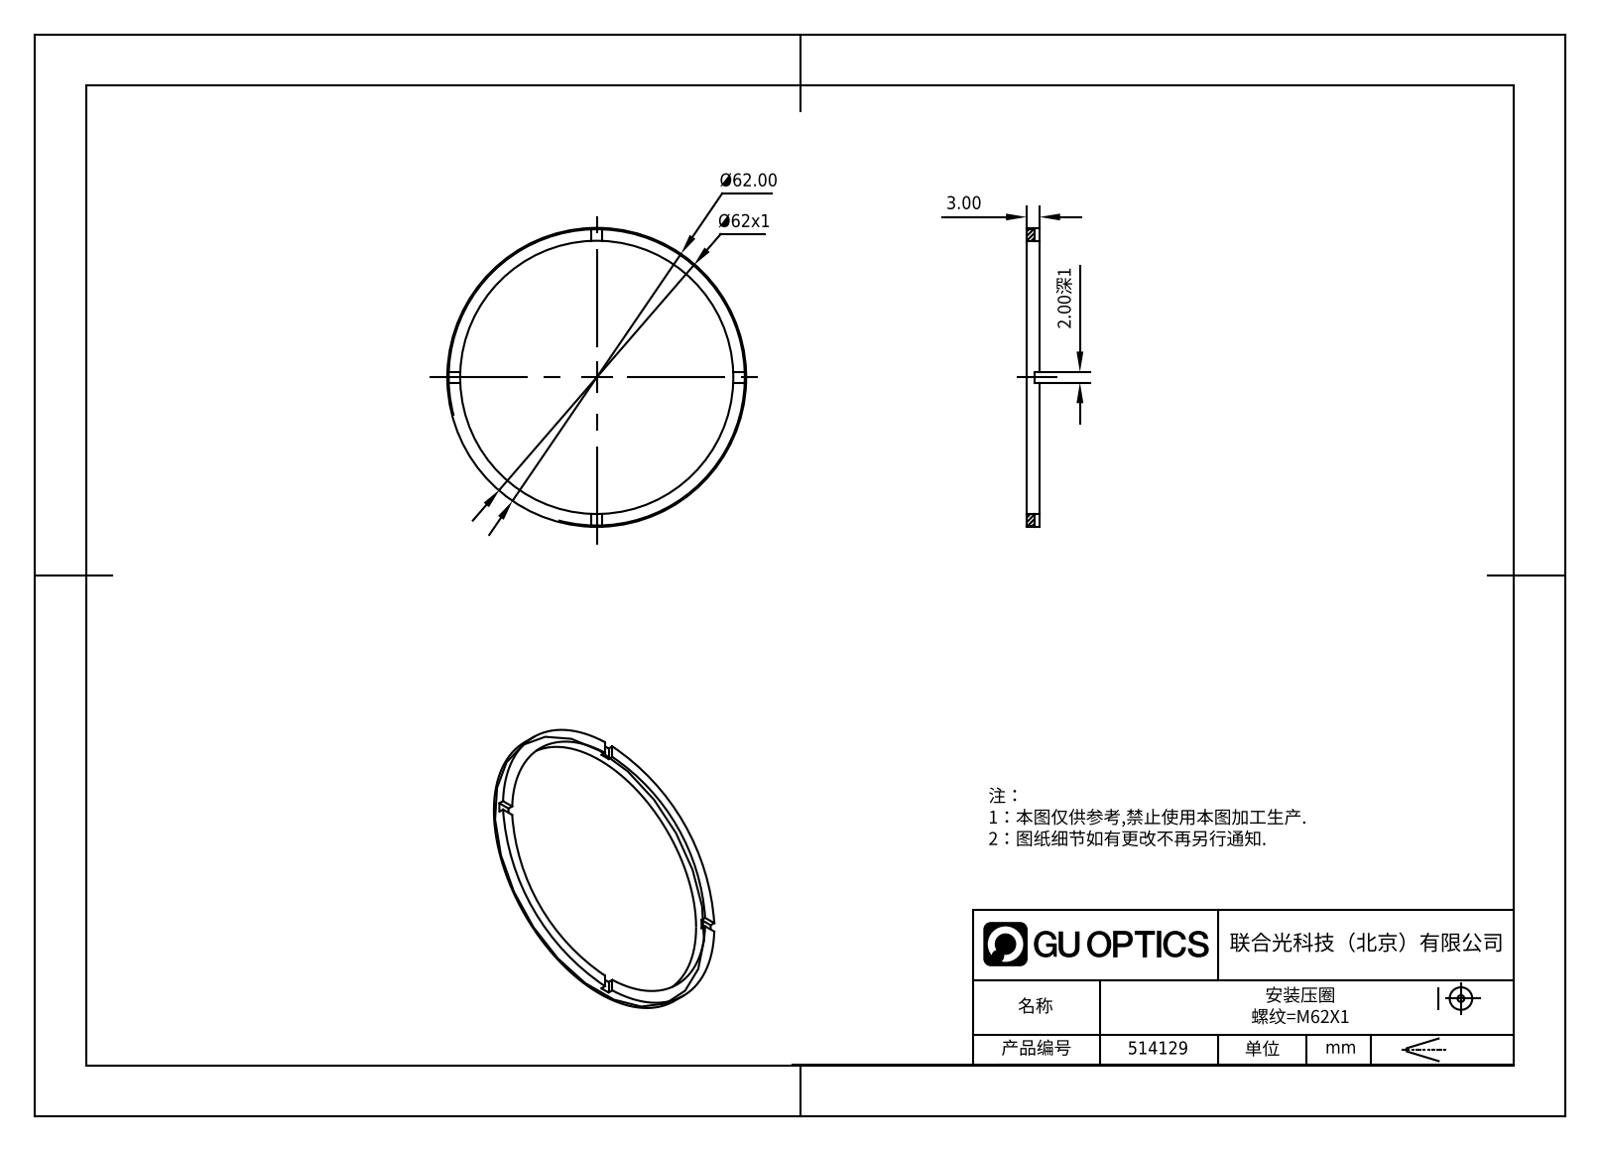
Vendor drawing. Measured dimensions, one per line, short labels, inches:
name: 514129
written by: SolidWorks 2020 (CONFIG_CONTROL_DESIGN)
unit: in
bodies: 1 solid, 21 faces (17 planar, 4 cylindrical, 0 other)
size: 2.441 × 2.441 × 0.118
volume: 0.084 in³; area: 3.193 in²
holes: 1× ⌀2.244
bosses: 1× ⌀2.441
face distances: 0.118, 0.079, 0.039
